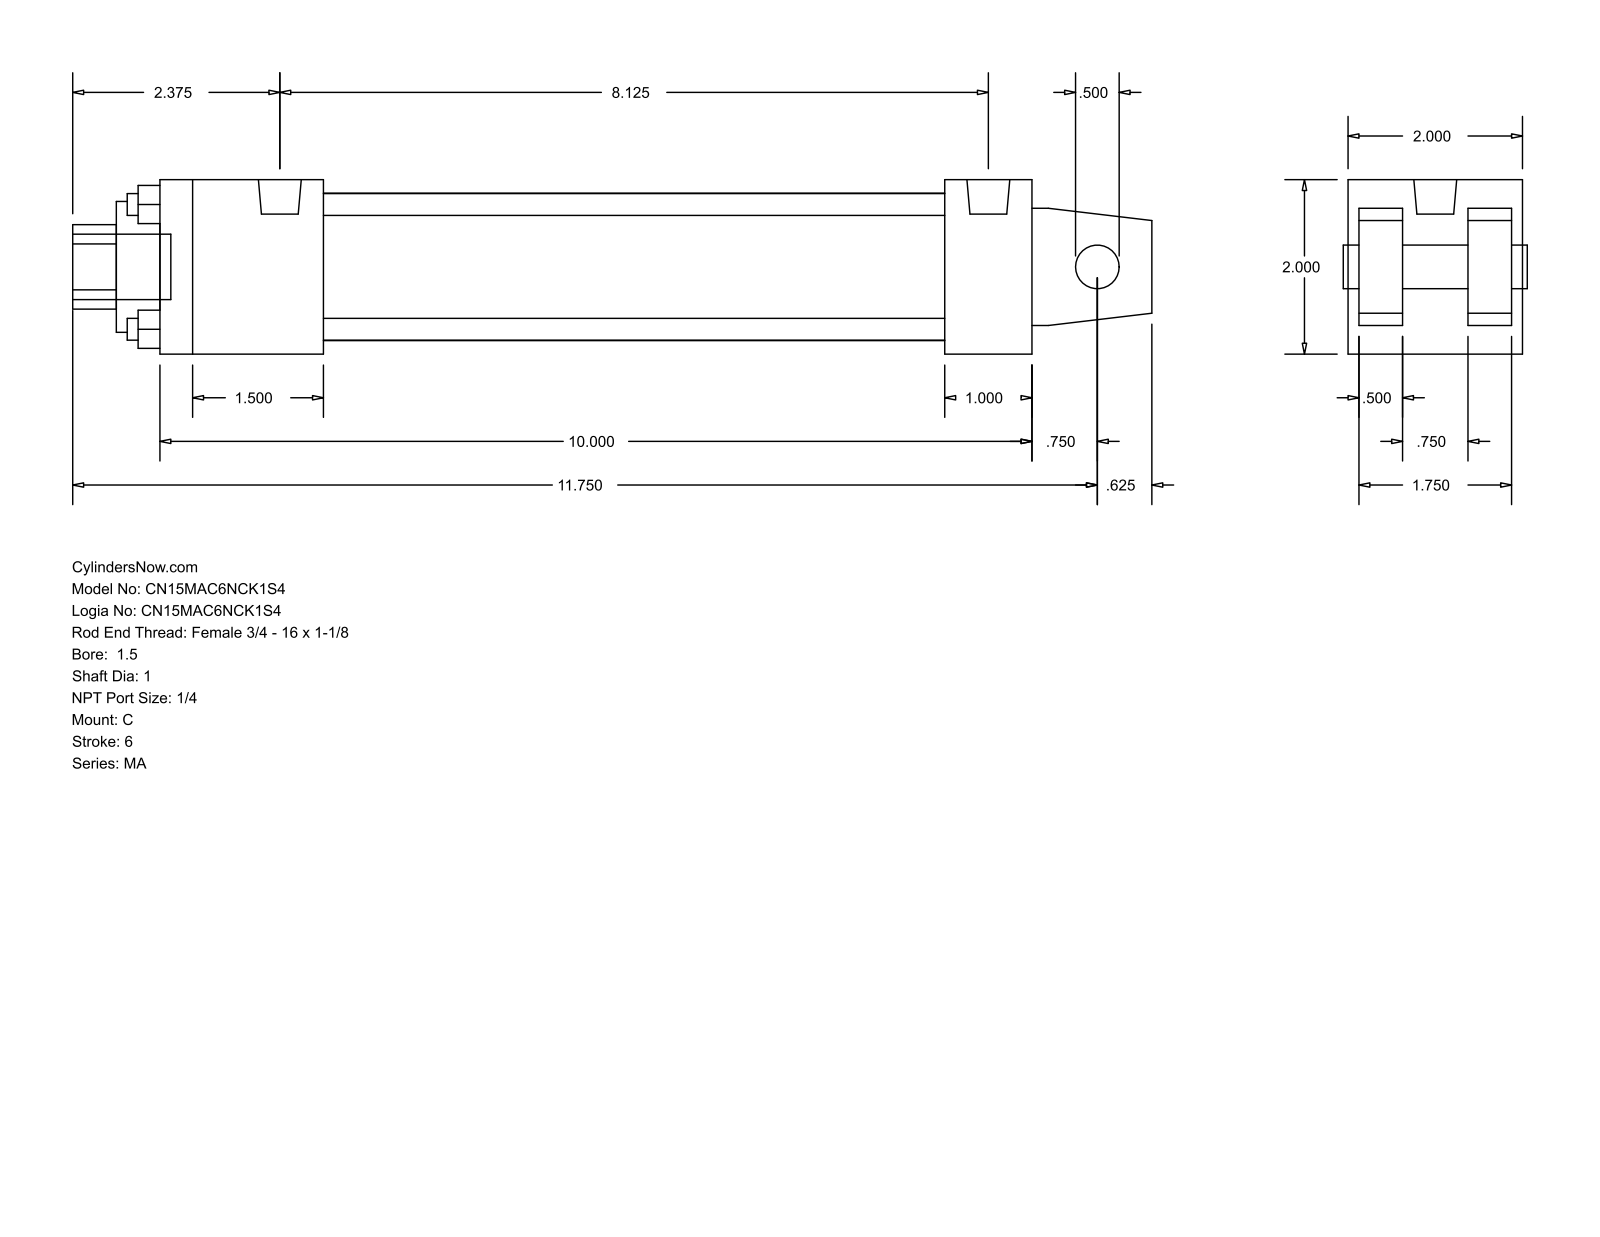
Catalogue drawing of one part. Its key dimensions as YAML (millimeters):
part_name: "MA_C__0150_1"
step_written_by: "GSSL Pune (CONFIG_CONTROL_DESIGN)"
units: millimeters
bodies: {solids: 0, faces: 103, planar: 76, cylindrical: 27, other: 0}
overall_size: [314.32, 50.8, 50.8]
round_holes:
  - {diameter: 6.35, count: 4}
  - {diameter: 12.7, count: 1}
  - {diameter: 25.4, count: 1}
  - {diameter: 38.1, count: 1}
  - {diameter: 42.93, count: 1}
round_bosses_or_shafts:
  - {diameter: 7.94, count: 4}
  - {diameter: 12.49, count: 2}
  - {diameter: 19.05, count: 1}
partial_cylinders:
  - {radius: 12.29, count: 1}
face_to_face_distances: [50.8, 47.63, 12.7, 3.17, 15.87, 34.93, 31.76, 44.46, 254, 25.4]
hole_center_spacings: [25.68, 36.32, 51.36]
